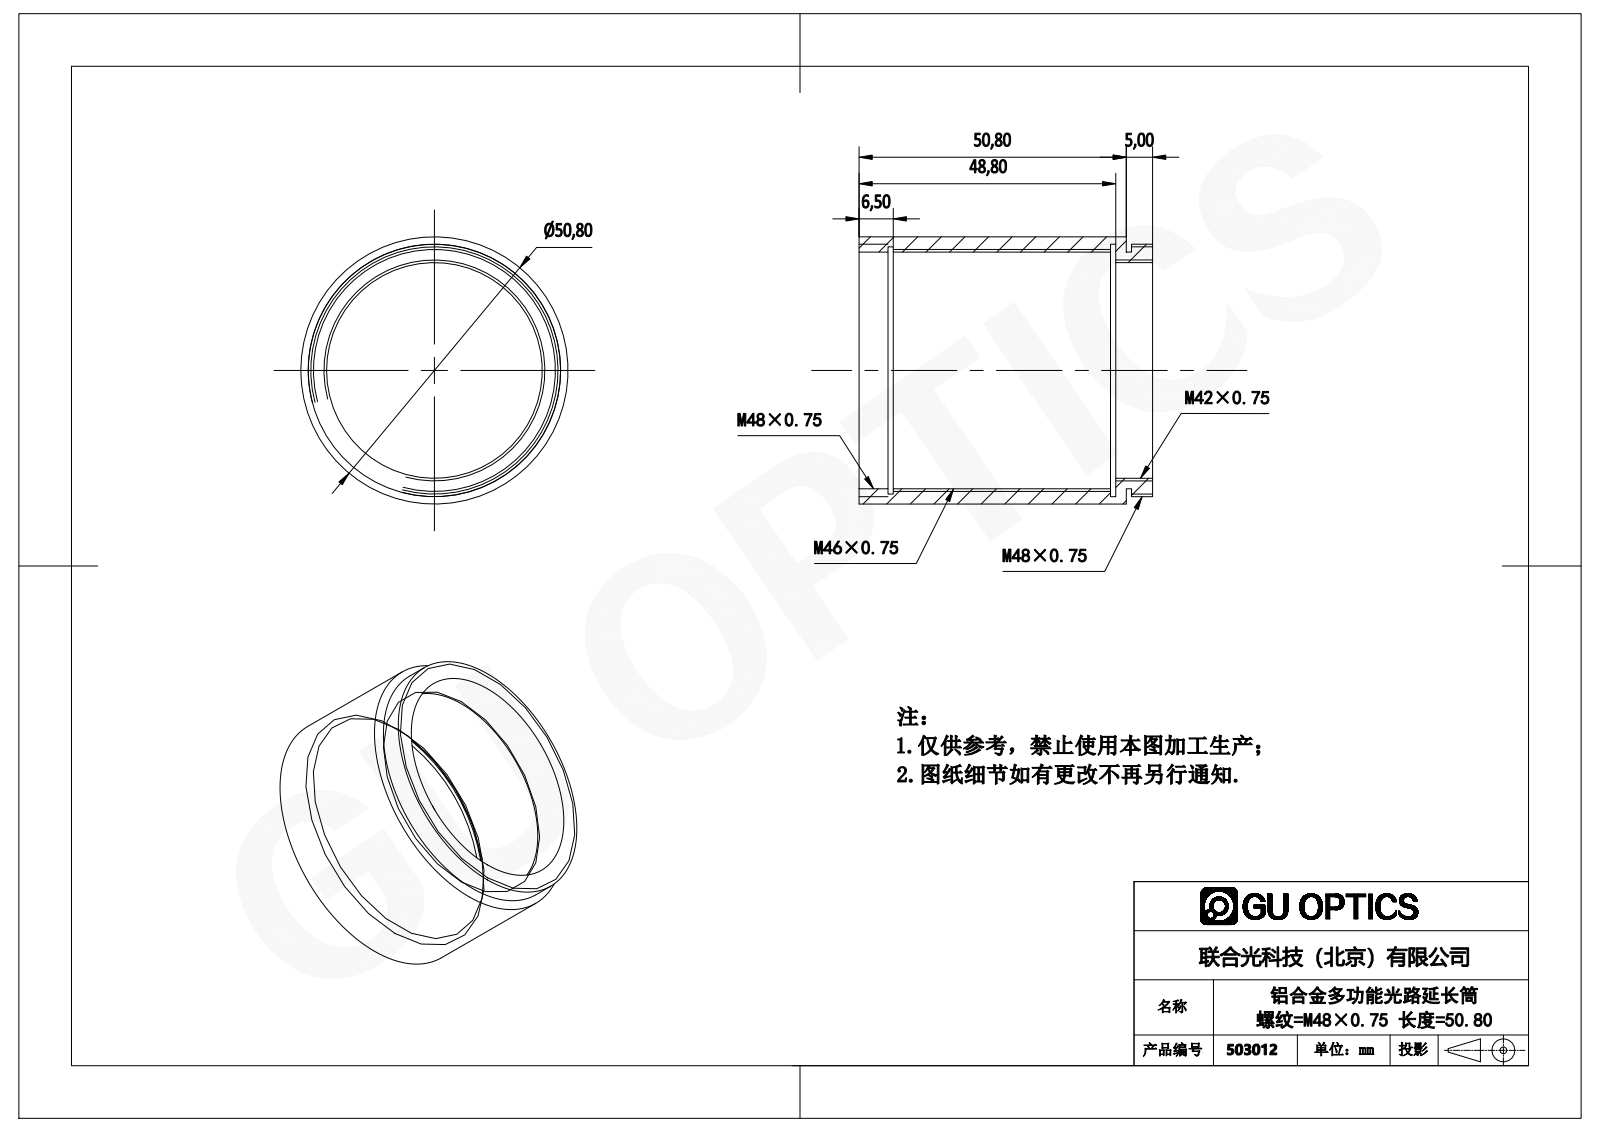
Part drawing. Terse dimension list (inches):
name: 503012
written by: SolidWorks 2016 (AUTOMOTIVE_DESIGN)
unit: in
bodies: 1 solid, 24 faces (8 planar, 16 cylindrical, 0 other)
size: 2.197 × 2 × 2
volume: 1.5 in³; area: 29.83 in²
holes: 1× ⌀1.614, 1× ⌀1.772, 1× ⌀1.85, 1× ⌀1.89
bosses: 1× ⌀2
face distances: 0.039, 0.276, 0.118, 0.157, 0.079, 0.197, 1.921, 2, 2.197, 1.665
